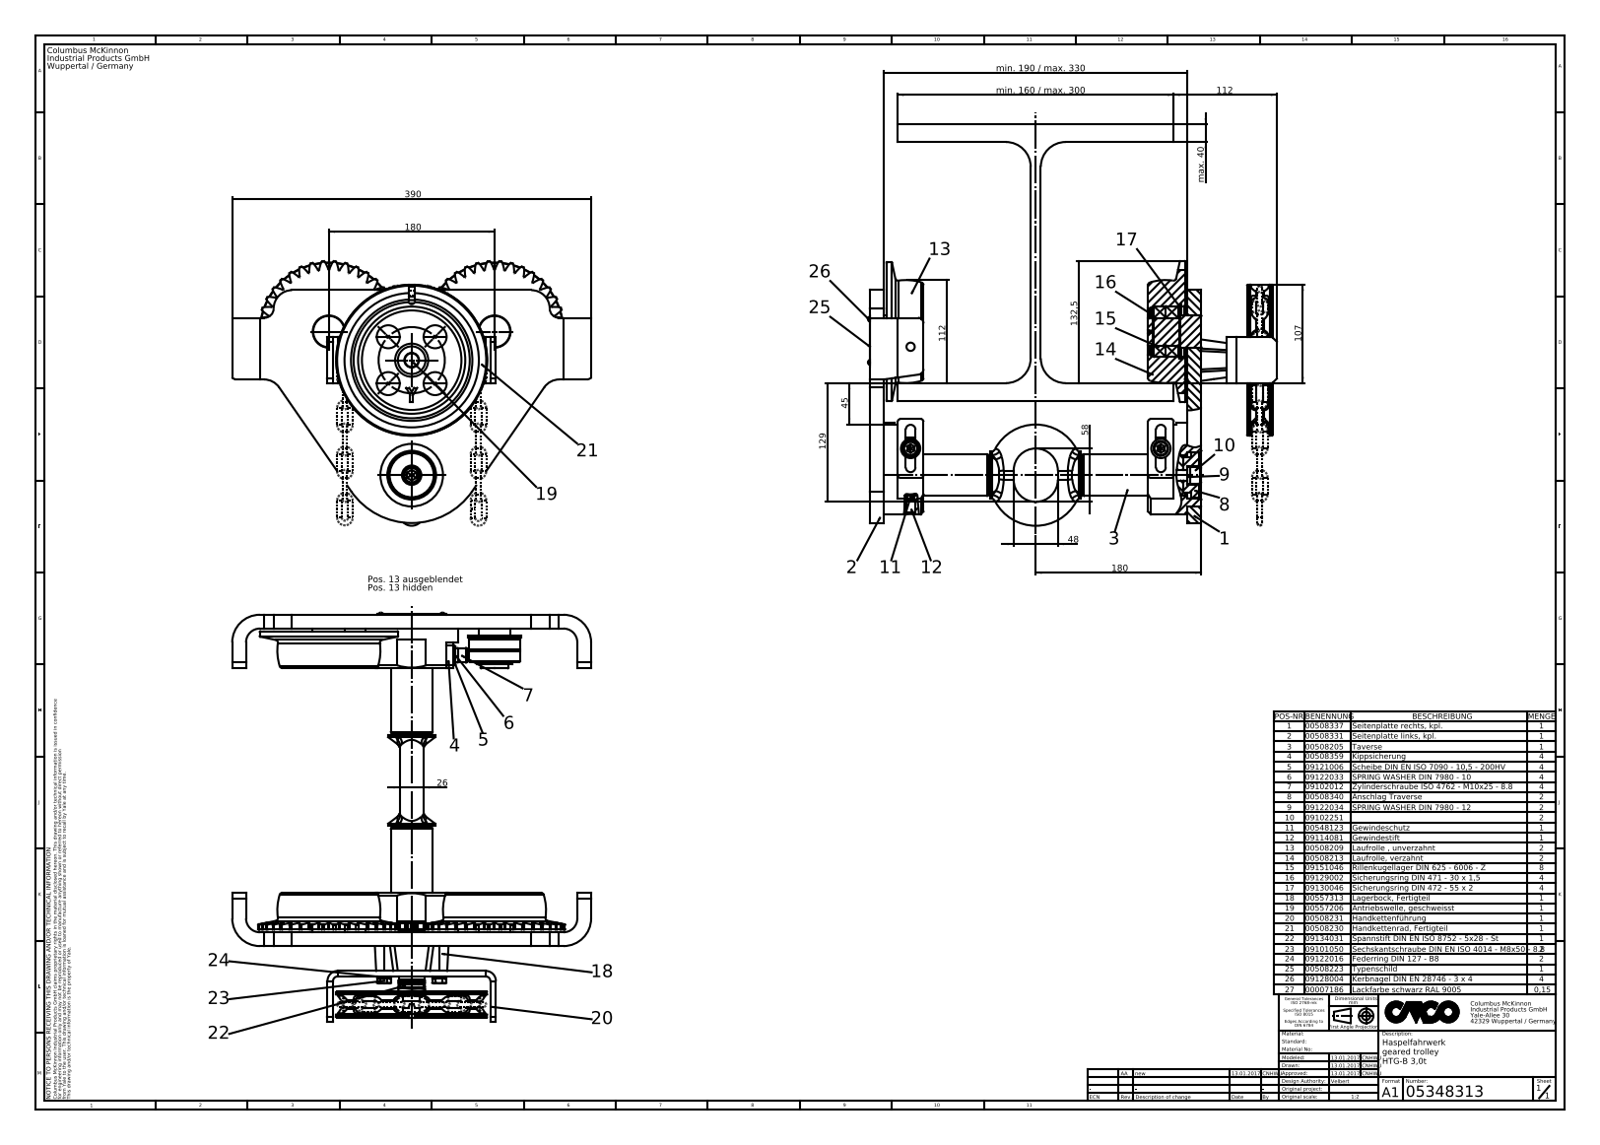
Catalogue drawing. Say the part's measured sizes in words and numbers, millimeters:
The part is named "HTG-B 3,0t". Its 3-D file was written by "SolidWorks 2015 (AUTOMOTIVE_DESIGN)". It is 0 solids with 928 faces: 282 planar, 372 cylindrical and 274 other. Overall it measures 444.4 by 436 by 390 millimeters. Round holes: 4 of diameter 25, 2 of diameter 9, 2 of diameter 35, 2 of diameter 48, 2 of diameter 49.5, 1 of diameter 6, 1 of diameter 8.5, 1 of diameter 16, 1 of diameter 20, 1 of diameter 50. Round bosses or shafts: 26 of diameter 5, 3 of diameter 30, 2 of diameter 150, 2 of diameter 38.6, 2 of diameter 21, 2 of diameter 16, 2 of diameter 10, 1 of diameter 164. Partial cylindrical surfaces (rounded edges, fillets, slot ends): 102 of radius 25, 9 of radius 1.5, 6 of radius 3, 4 of radius 5.25, 4 of radius 6, 4 of radius 10, 4 of radius 15, 4 of radius 20. The main face-to-face distances are 19, 281, 15, 300, 345, 174.5, 185.5, 159.5, 170.5, 330. The hole center spacings are 36.01, 50.92, 25.86, 61.02, 64.78, 72.01, 85.8, 90.01.
